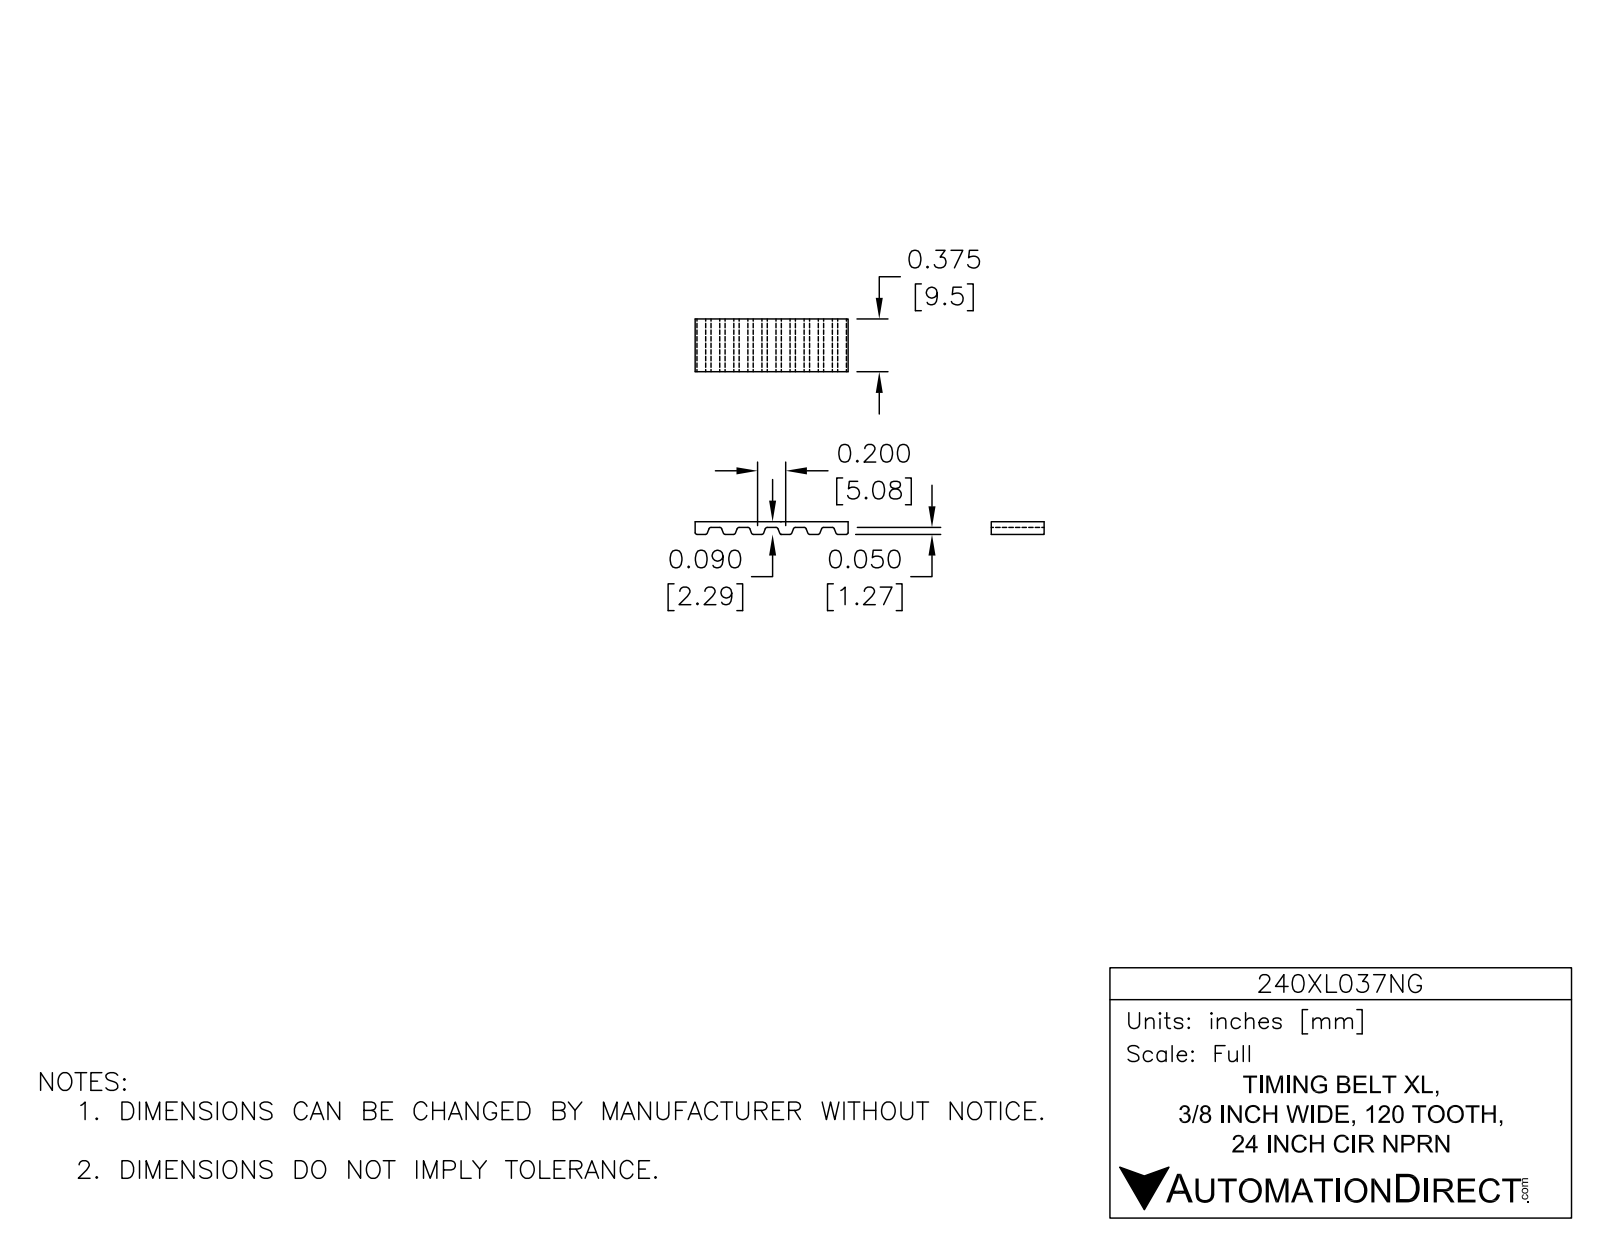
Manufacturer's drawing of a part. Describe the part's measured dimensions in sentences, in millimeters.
The part is named "240XL037NG". Its 3-D file was written by "SolidWorks 2014 (AUTOMOTIVE_DESIGN)". It is 1 solid with 1000 faces: 440 planar, 560 cylindrical and 0 other. Overall it measures 261.3 by 76.2 by 9.5 millimeters. Its volume is 8 030 cubic millimeters and its surface area 14 840 square millimeters. Partial cylindrical surfaces (rounded edges, fillets, slot ends): 480 of radius 0.4, 2 of radius 37.1, 2 of radius 38.1. The main face-to-face distances are 76.2, 1, 75.2, 74.2, 9.5, 2.3, 73.9, 1.3, 72.9, 71.6.
